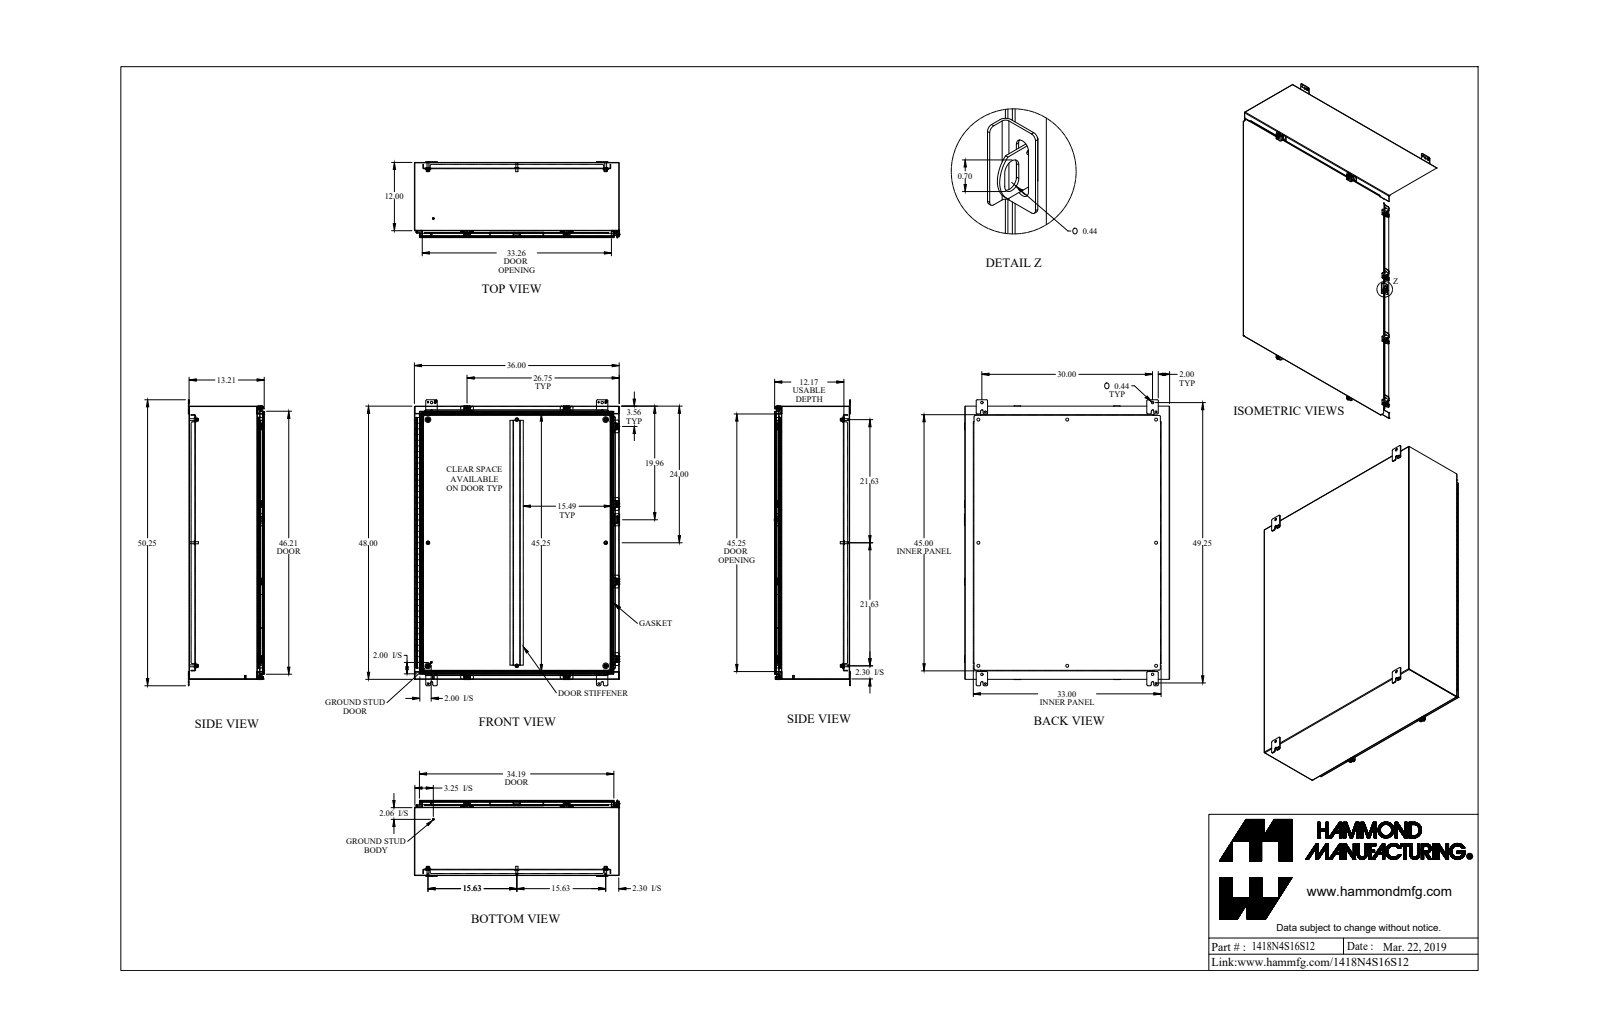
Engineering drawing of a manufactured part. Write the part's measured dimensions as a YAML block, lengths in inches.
part_name: "1418N4S16S12_Default"
step_written_by: "SolidWorks 2019 (CONFIG_CONTROL_DESIGN)"
units: inches
bodies: {solids: 66, faces: 2103, planar: 1108, cylindrical: 853, other: 142}
overall_size: [50.25, 36.063, 13.375]
volume: 608.6
surface_area: 15906
round_holes:
  - {diameter: 0.213, count: 8}
  - {diameter: 0.265, count: 8}
  - {diameter: 0.375, count: 8}
  - {diameter: 0.5, count: 8}
  - {diameter: 0.307, count: 4}
  - {diameter: 0.313, count: 4}
  - {diameter: 0.437, count: 4}
  - {diameter: 0.445, count: 4}
  - {diameter: 0.11, count: 1}
  - {diameter: 0.125, count: 1}
round_bosses_or_shafts:
  - {diameter: 0.65, count: 8}
  - {diameter: 0.5, count: 8}
  - {diameter: 0.39, count: 8}
  - {diameter: 0.375, count: 8}
  - {diameter: 0.332, count: 8}
  - {diameter: 0.244, count: 8}
  - {diameter: 1, count: 4}
  - {diameter: 0.313, count: 2}
partial_cylinders:
  - {radius: 0.25, count: 44}
  - {radius: 0.048, count: 39}
  - {radius: 0.143, count: 39}
  - {radius: 0.188, count: 30}
  - {radius: 0.036, count: 22}
  - {radius: 0.108, count: 22}
  - {radius: 0.141, count: 16}
  - {radius: 0.125, count: 14}
face_to_face_distances: [0.072, 13.066, 13.138, 0.072, 0.095, 13.138, 13.21, 0.937, 1.009, 12.106]
hole_center_spacings: [38.003, 51.507, 7.196, 15.625, 21.625, 24.468, 45.893, 45.986]
